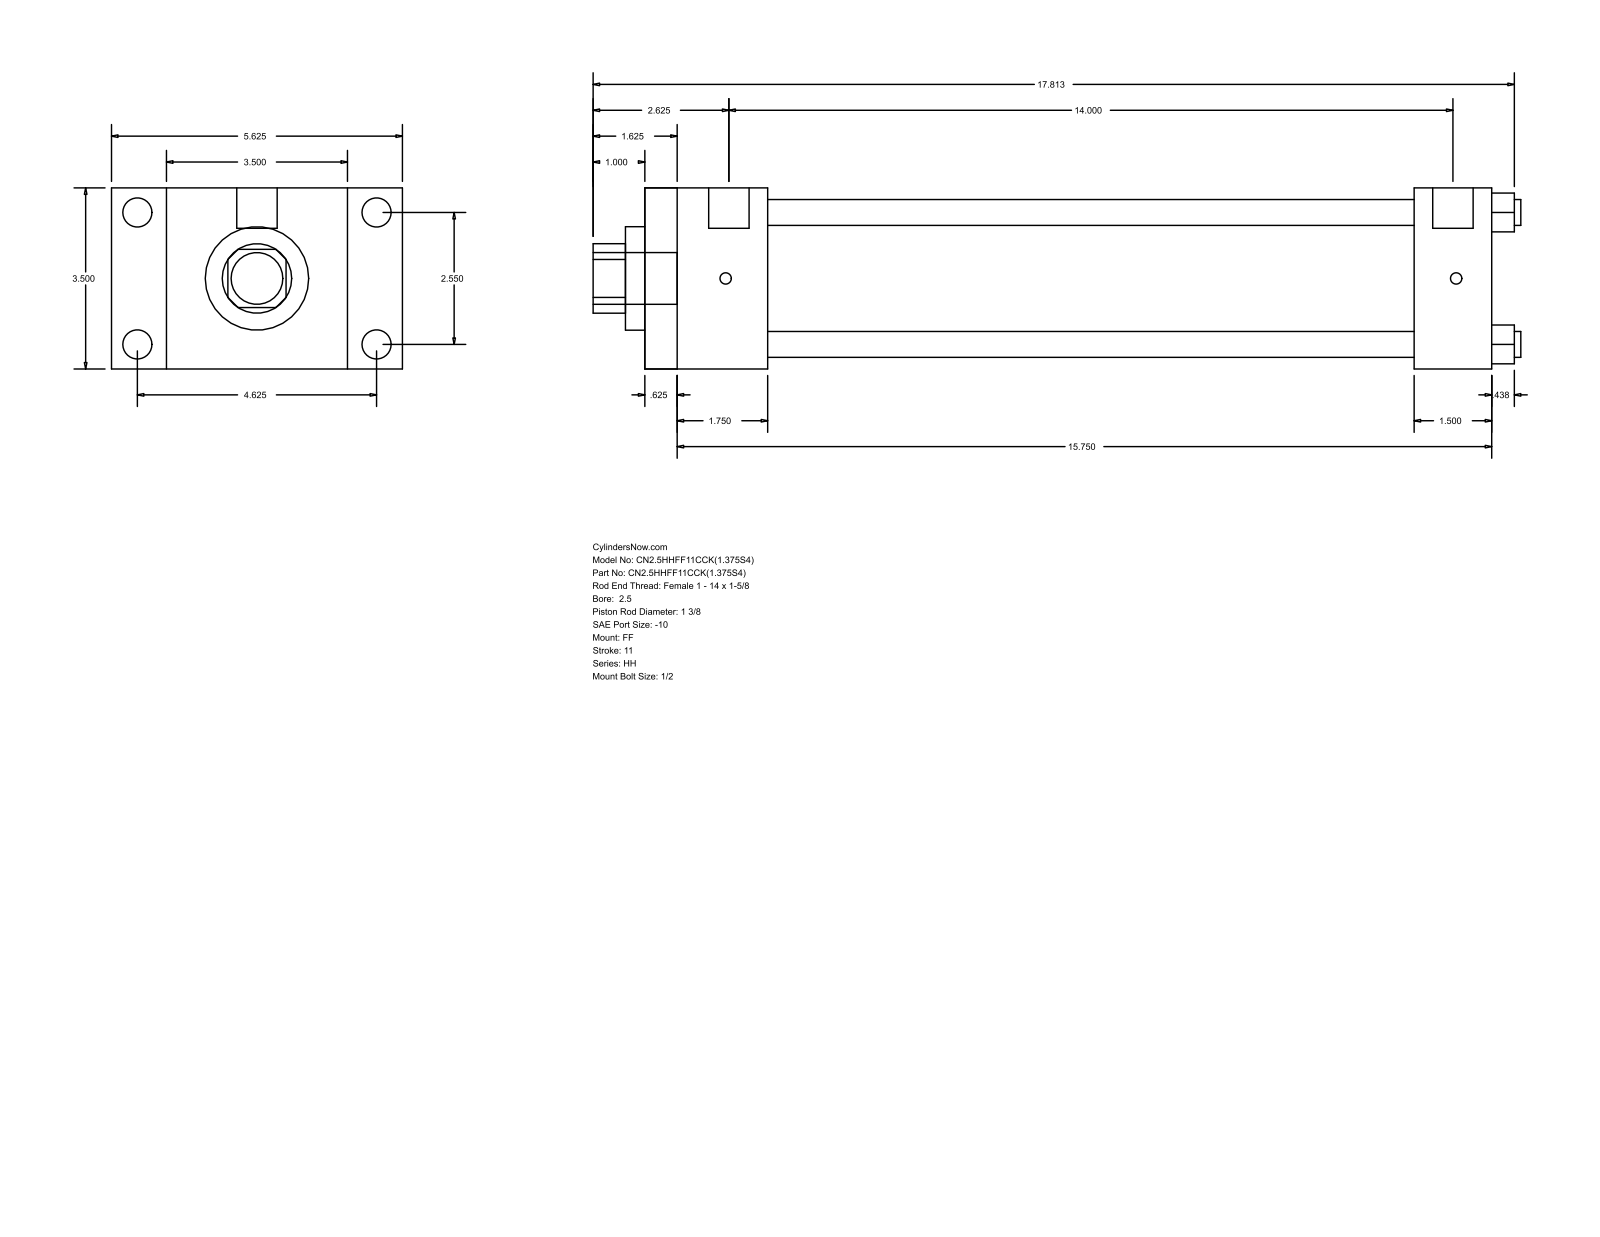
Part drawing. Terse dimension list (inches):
name: HH_FF__0250_1.375
written by: GSSL Pune (CONFIG_CONTROL_DESIGN)
unit: in
bodies: 0 solids, 92 faces (64 planar, 28 cylindrical, 0 other)
size: 17.937 × 5.625 × 3.5
holes: 4× ⌀0.5, 1× ⌀1.375, 1× ⌀2, 1× ⌀2.875
bosses: 4× ⌀0.563, 4× ⌀0.219, 2× ⌀0.781, 1× ⌀1
rounds: 1× R0.672
face distances: 3.5, 16.375, 0.625, 15.75, 2.375, 1.75, 14, 14.875, 14.25, 12.5
hole spacings: 1.803, 2.55, 3.606
